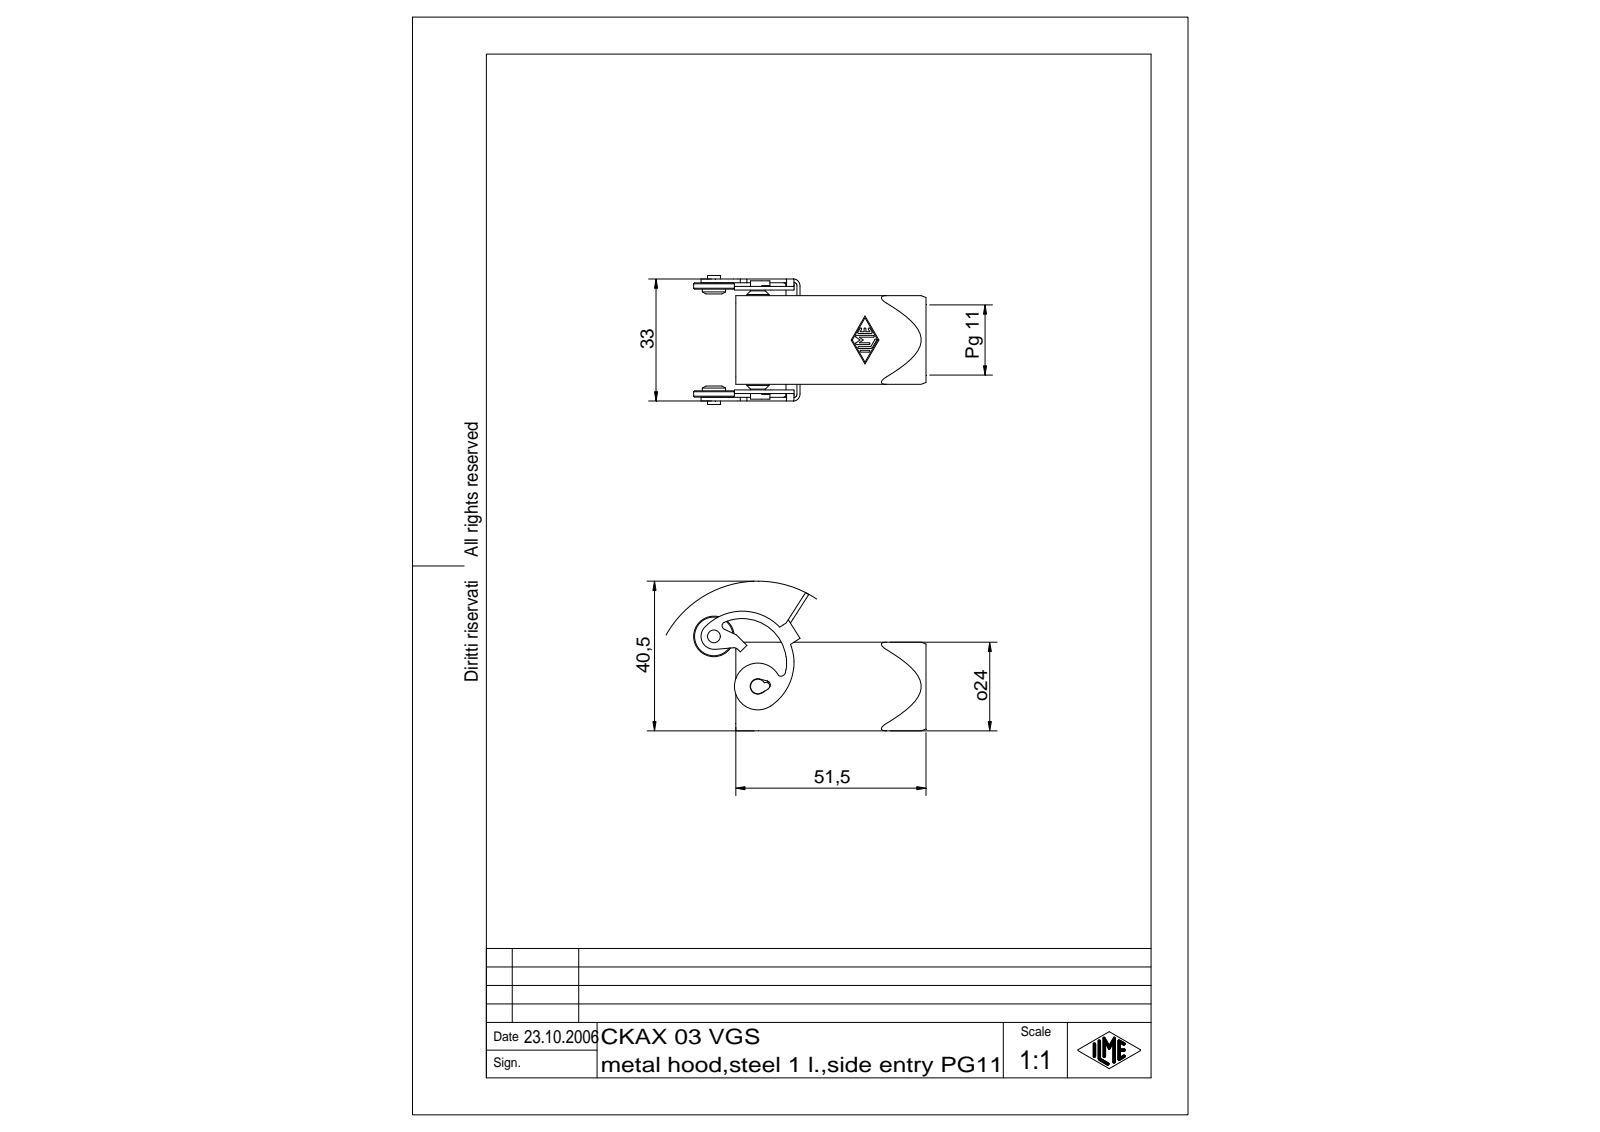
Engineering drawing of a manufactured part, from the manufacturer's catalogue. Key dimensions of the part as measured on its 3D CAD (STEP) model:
Part name (STEP PRODUCT): CKAX 03 VGS
STEP written by: Autodesk Inventor 7 (AUTOMOTIVE_DESIGN)
Units: millimetres
Bodies: 2 solids, 237 faces (81 planar, 90 cylindrical, 66 other)
Overall size (bounding box): 62.9 × 37.42 × 34.9
Volume: 8 845 mm³ · Surface area: 12 105 mm²
Round holes (diameter × count): ⌀3.3 ×1, ⌀15 ×1, ⌀17.26 ×1
Round bosses / shafts (diameter × count): ⌀11 ×1, ⌀6.3 ×1, ⌀6 ×1, ⌀4 ×1, ⌀3.5 ×1
Partial cylindrical surfaces — rounded edges, fillets, slot ends (radius × count): R2 ×18, R0.25 ×14, R1 ×6, R0.8 ×2, R1.1 ×1, R1.25 ×1, R1.5 ×1, R2.1 ×1
Main face-to-face distances: 1, 23, 24, 22, 2, 3, 2.5, 25.5, 3.5, 26.5
